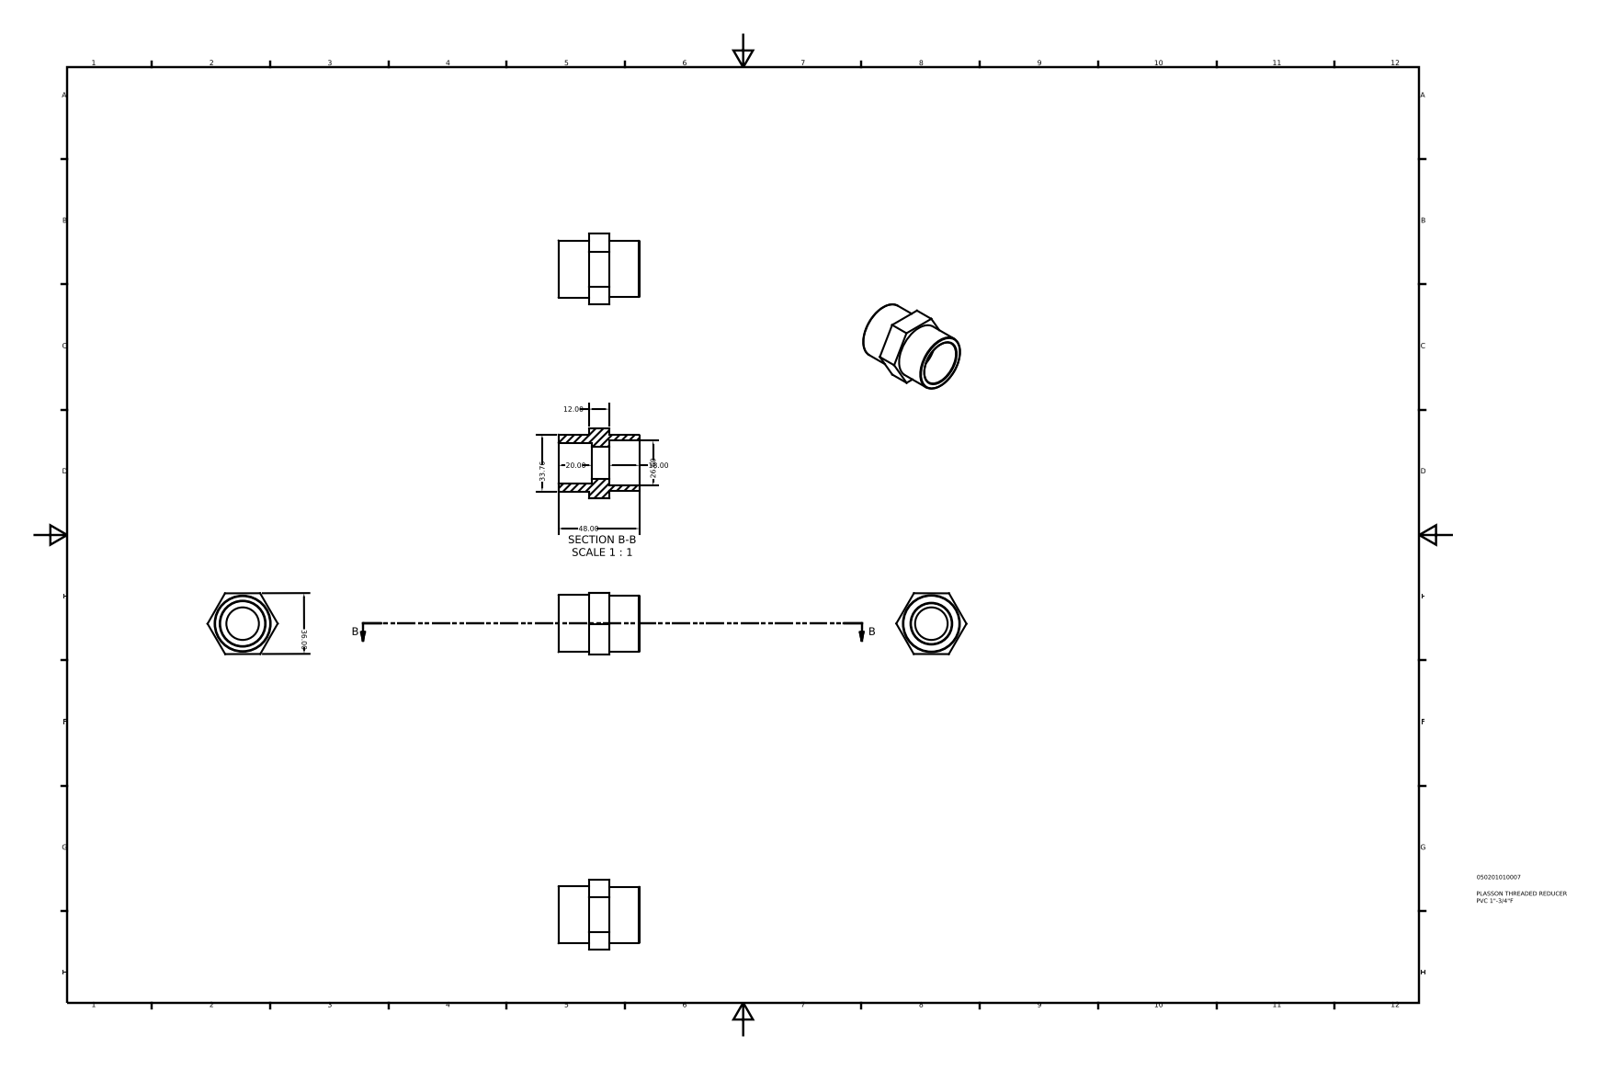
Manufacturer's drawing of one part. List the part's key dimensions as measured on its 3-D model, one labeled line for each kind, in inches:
Part name (STEP PRODUCT): 050201010007
STEP written by: Autodesk Inventor 2015 (AUTOMOTIVE_DESIGN)
Units: inches
Bodies: 1 solid, 21 faces (12 planar, 5 cylindrical, 4 other)
Overall size (bounding box): 1.89 × 1.637 × 1.42
Volume: 1.412 in³ · Surface area: 16.3 in²
Round holes (diameter × count): ⌀0.759 ×1, ⌀0.95 ×1, ⌀1.047 ×1
Round bosses / shafts (diameter × count): ⌀1.329 ×1, ⌀1.309 ×1
Main face-to-face distances: 1.181, 1.418, 0.709, 1.89, 1.417, 0.472, 0.787, 0.079, 0.394, 1.102
